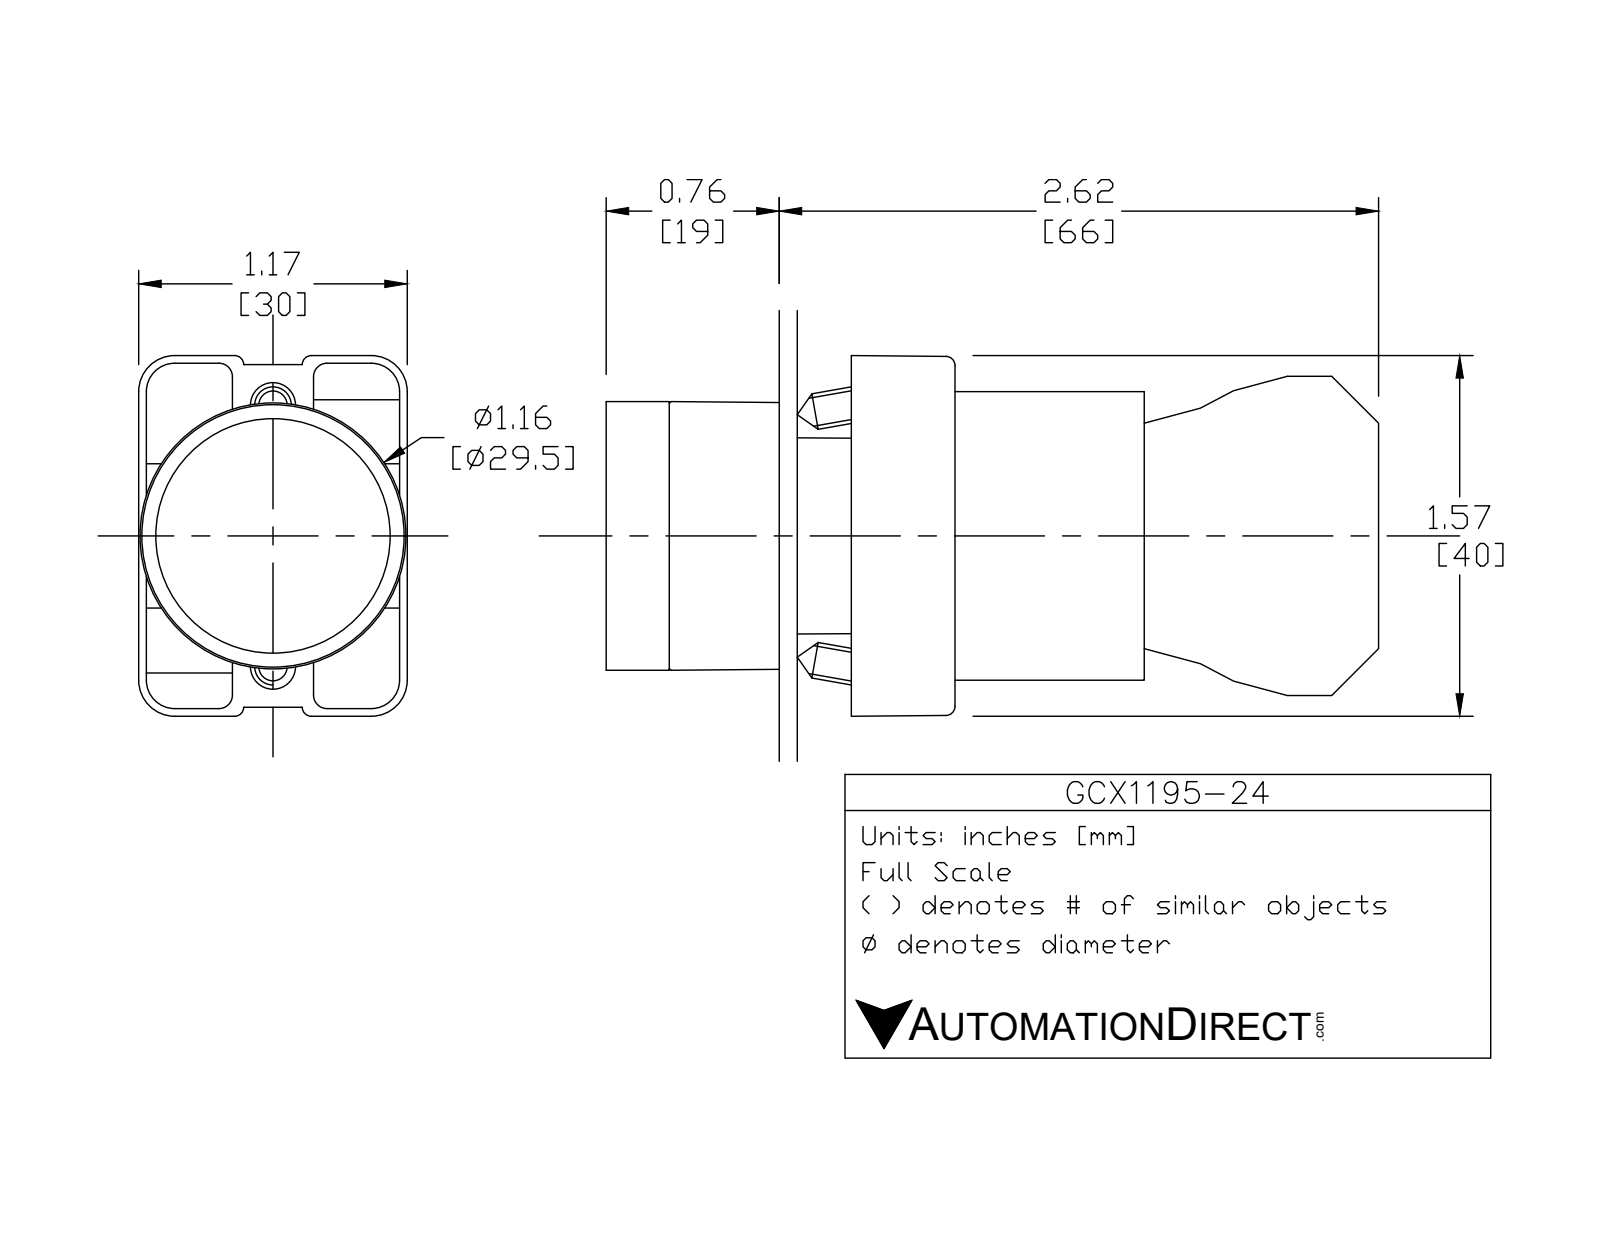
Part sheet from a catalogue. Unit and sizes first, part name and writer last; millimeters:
Units: millimetres
Overall size (bounding box): 84.3 × 40.2 × 29.9
Round holes (diameter × count): ⌀2 ×2, ⌀3.1 ×2, ⌀3.3 ×2, ⌀2.2 ×1, ⌀5 ×1, ⌀11.9 ×1, ⌀22.3 ×1, ⌀22.6 ×1, ⌀26 ×1
Round bosses / shafts (diameter × count): ⌀4 ×4, ⌀29.8 ×1, ⌀25.5 ×1, ⌀24 ×1, ⌀21.7 ×1, ⌀19.8 ×1, ⌀12.8 ×1
Partial cylindrical surfaces — rounded edges, fillets, slot ends (radius × count): R1.5 ×24, R1 ×12, R3.1 ×12, R4 ×12, R1 ×8, R3.3 ×2, R0.5 ×1, R1.6 ×1
Main face-to-face distances: 21, 51.3, 30.3, 14.7, 29.7, 0.8, 7, 0.8, 19, 14.6
Hole centre spacings: 6, 13.8, 12, 12.4
Volume: 45 790 mm³ · Surface area: 25 000 mm²
Bodies: 8 solids, 431 faces (252 planar, 148 cylindrical, 31 other)
Part name (STEP PRODUCT): ecx1029; GCX1195-24; ecx1040; GCX1195 OPERATOR (+1 more)
STEP written by: SolidWorks 2016 (AUTOMOTIVE_DESIGN)
